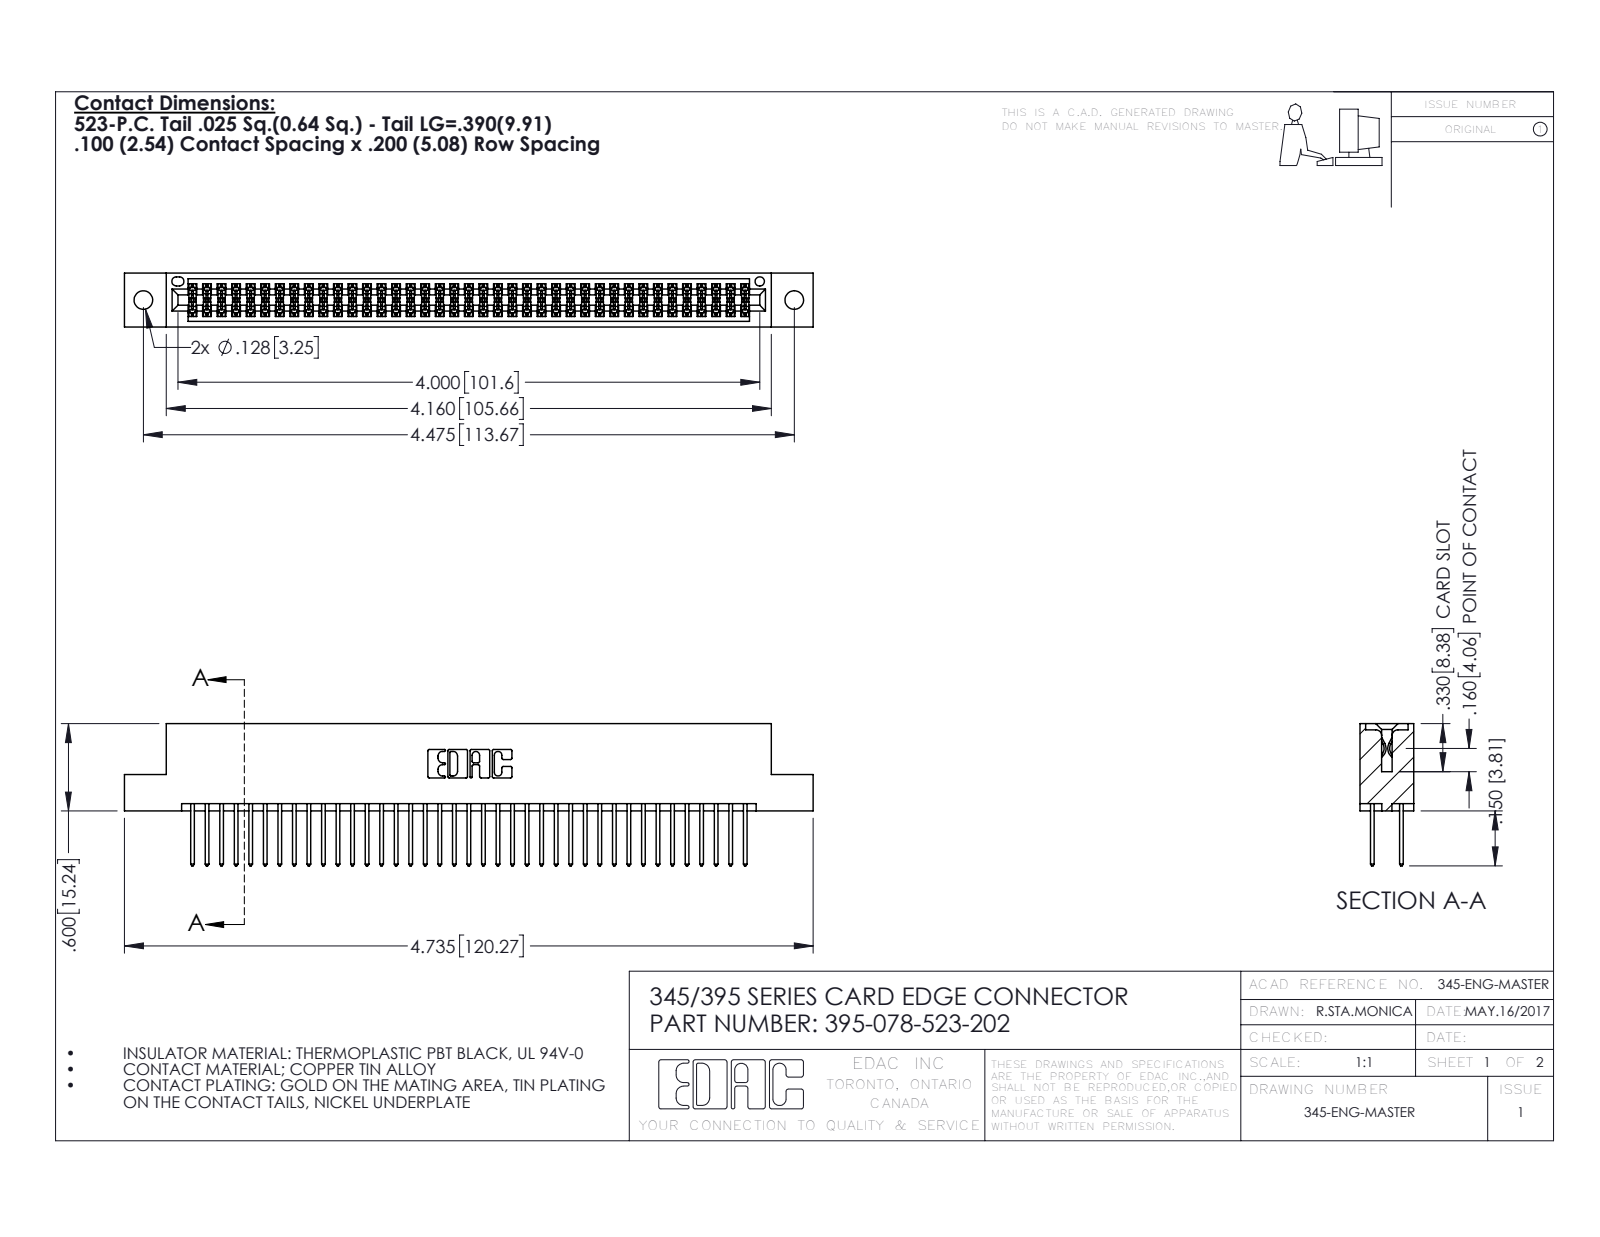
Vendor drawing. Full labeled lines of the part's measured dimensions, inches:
Part name (STEP PRODUCT): 395-078-523-202; 345-292-001_345-293-123; 345 Part_Flush Mounting Lugs - 0.128 Dia
STEP written by: SolidWorks 2016 (CONFIG_CONTROL_DESIGN)
Units: inches
Bodies: 79 solids, 4026 faces (2654 planar, 1372 cylindrical, 0 other)
Overall size (bounding box): 4.735 × 0.977 × 0.37
Volume: 0.719 in³ · Surface area: 27.59 in²
Round holes (diameter × count): ⌀0.128 ×2, ⌀0.064 ×1
Partial cylindrical surfaces — rounded edges, fillets, slot ends (radius × count): R0.006 ×117, R0.01 ×78, R0.01 ×22, R0.007 ×6, R0.031 ×6, R0.026 ×3, R0.014 ×2, R0.019 ×2
Main face-to-face distances: 0.298, 0.072, 0.2, 0.098, 0.272, 0.025, 0.37, 0.225, 0.175, 0.149
Hole centre spacings: 0.27, 4.239, 4.475
